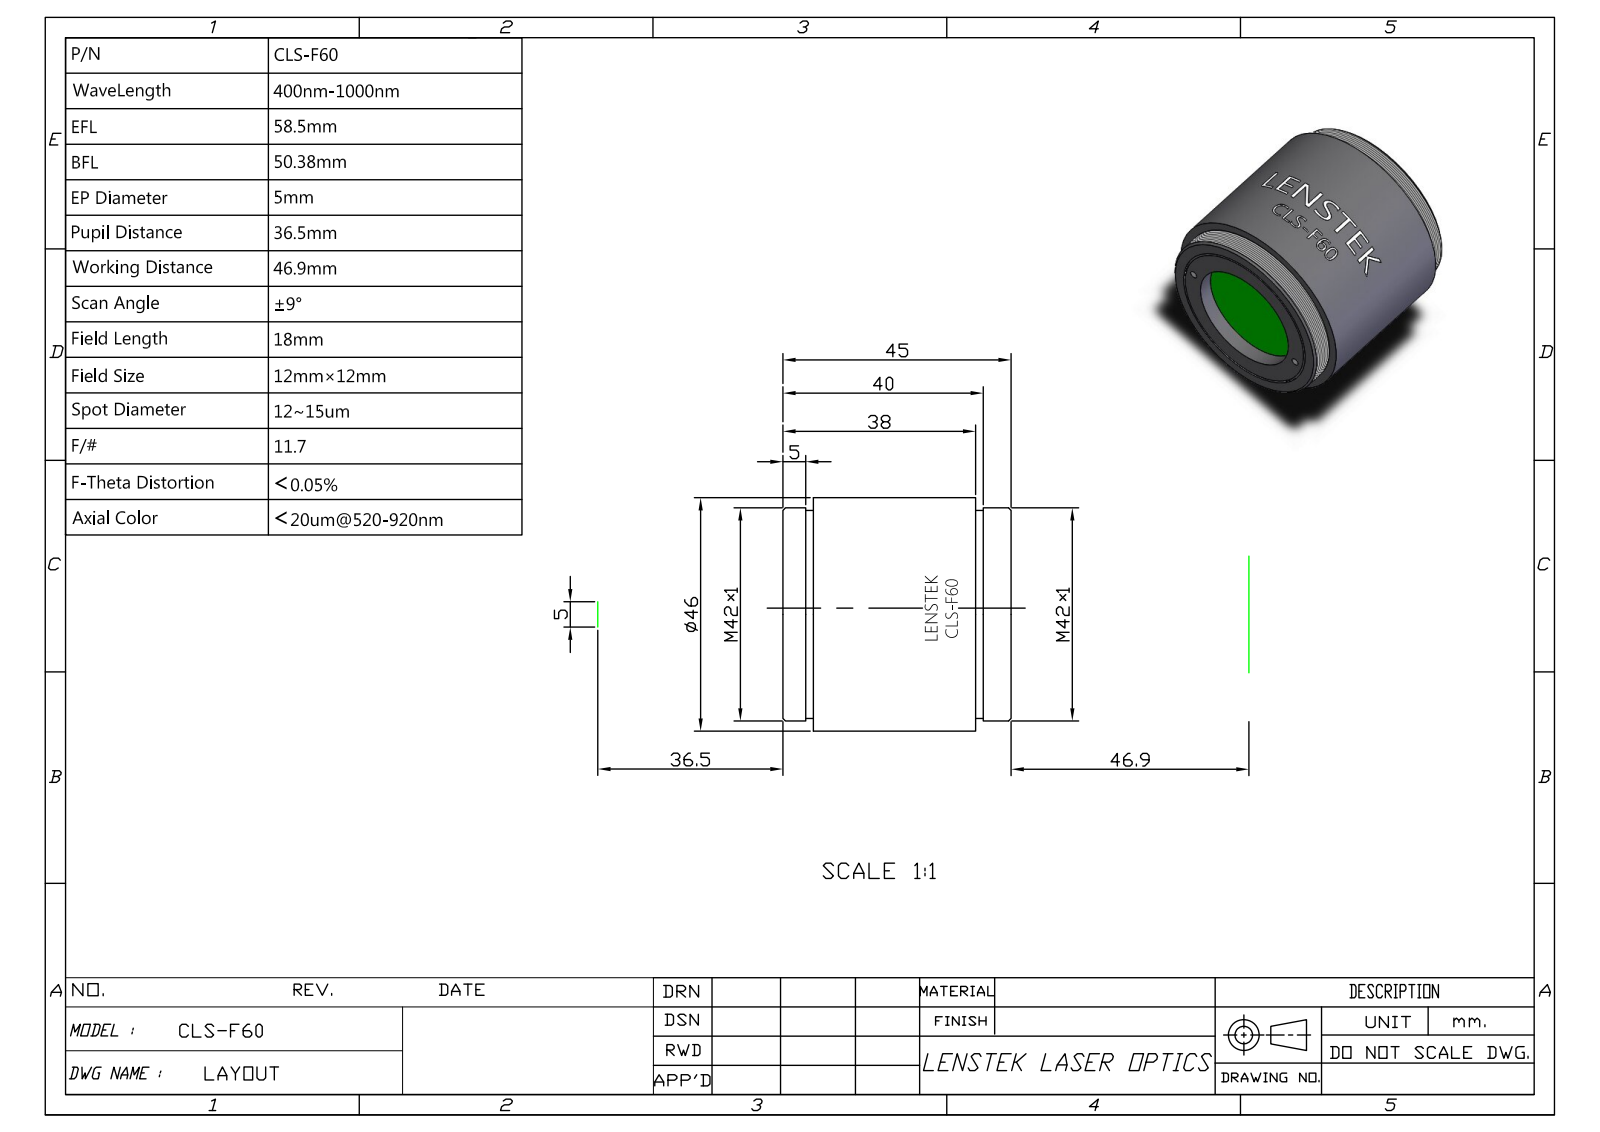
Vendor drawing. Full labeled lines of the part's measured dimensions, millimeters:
Part name (STEP PRODUCT): CLS-F60
STEP written by: SolidWorks 2018 (AUTOMOTIVE_DESIGN)
Units: millimetres
Bodies: 5 solids, 221 faces (97 planar, 44 cylindrical, 80 other)
Overall size (bounding box): 46 × 46 × 45
Volume: 35 501 mm³ · Surface area: 19 600 mm²
Round holes (diameter × count): ⌀1.8 ×2, ⌀26 ×1, ⌀35 ×1, ⌀36 ×1
Round bosses / shafts (diameter × count): ⌀46 ×1, ⌀42 ×1
Partial cylindrical surfaces — rounded edges, fillets, slot ends (radius × count): R22.99 ×1
Main face-to-face distances: 3.5, 41.5, 38, 45, 5, 40, 1.5, 36.5, 35, 0.56
Hole centre spacings: 15.5, 31
